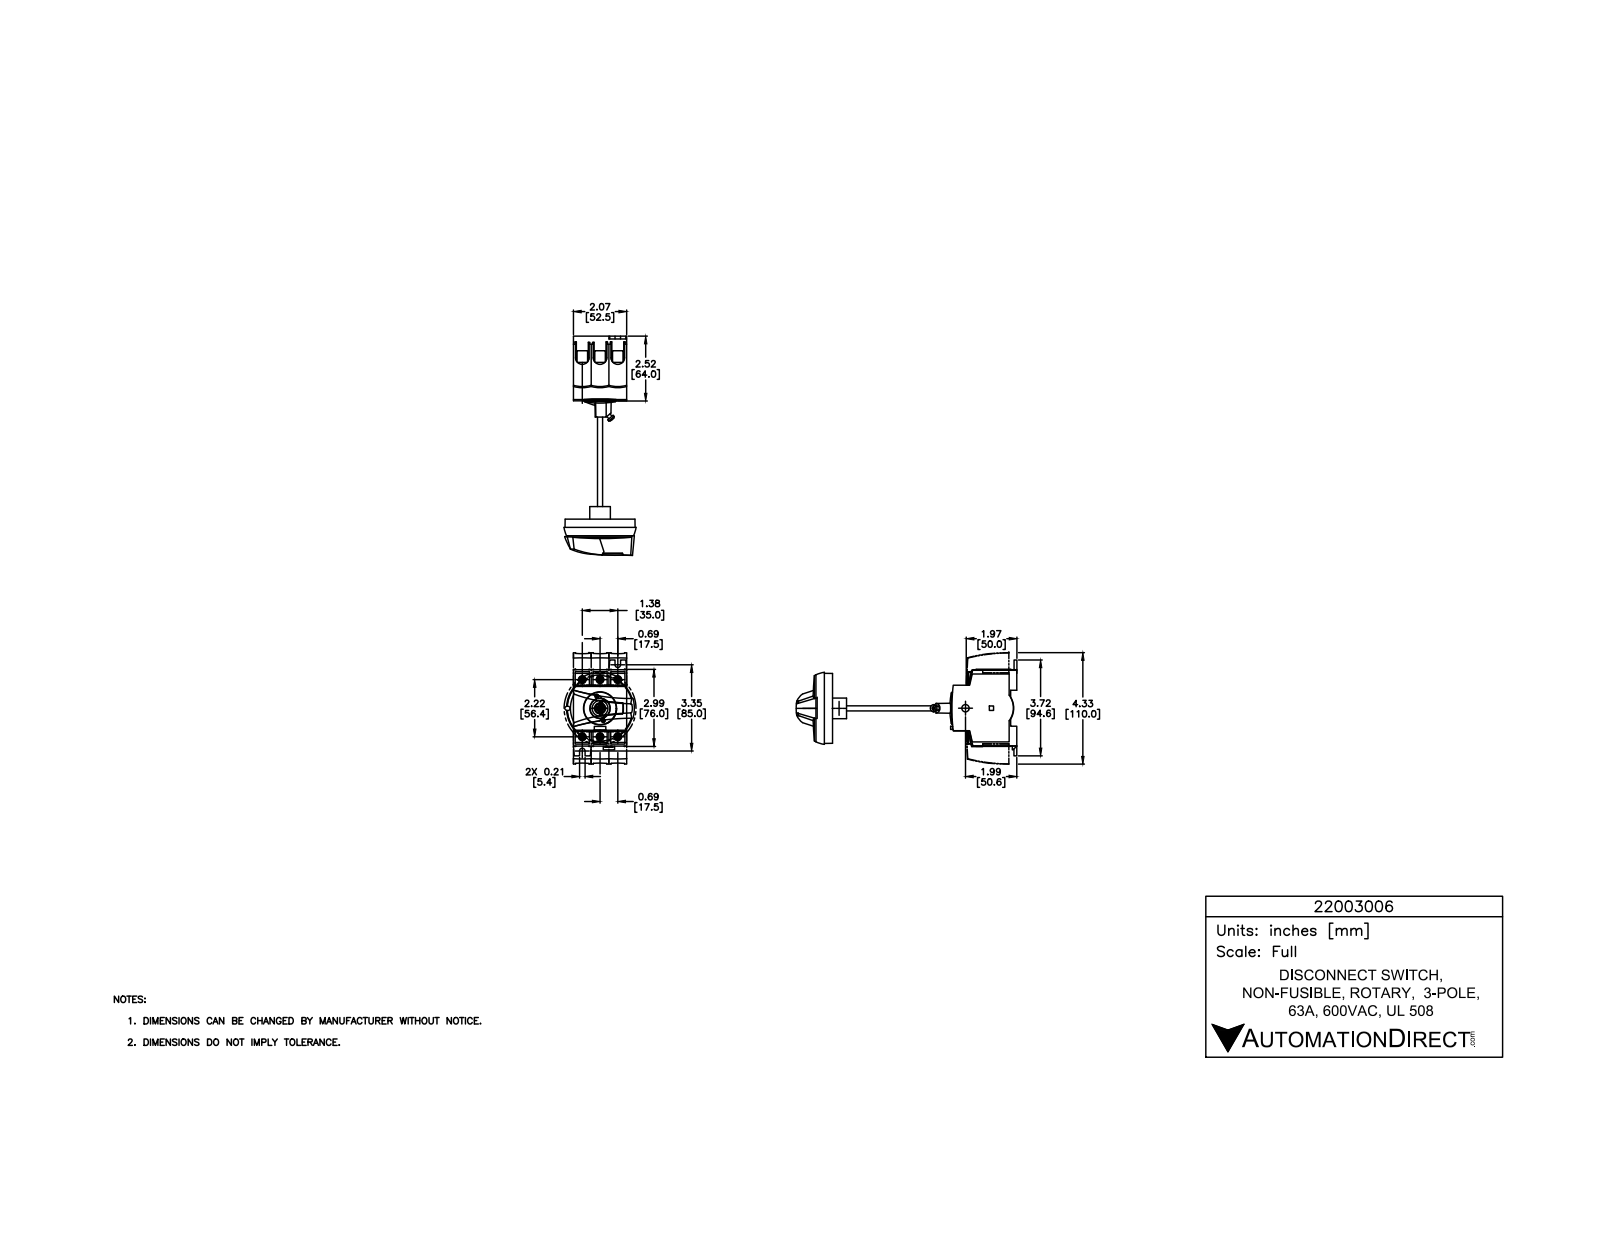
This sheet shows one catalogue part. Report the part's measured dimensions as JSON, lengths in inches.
{"part_name": "22003006-UL", "step_written_by": "SolidWorks 2021 (CONFIG_CONTROL_DESIGN)", "units": "inches", "bodies": {"solids": 1, "faces": 238, "planar": 199, "cylindrical": 39, "other": 0}, "overall_size": [3.724, 2.576, 2.067], "volume_in3": 12.81, "surface_area_in2": 42.15, "round_holes": [[0.26, 6], [0.283, 1], [1.26, 1]], "partial_cylinders_radius": [[1.18, 9], [0.012, 4], [0.106, 2], [0.37, 1], [0.827, 1], [7.862, 1]], "face_to_face_distances": [2.067, 2.969, 2.391, 2.382, 0.61, 0.142, 2.827, 0.587, 2.358, 1.772], "hole_center_spacings": [0.689, 1.307, 2.325, 2.22, 1.11, 1.378, 2.613]}
